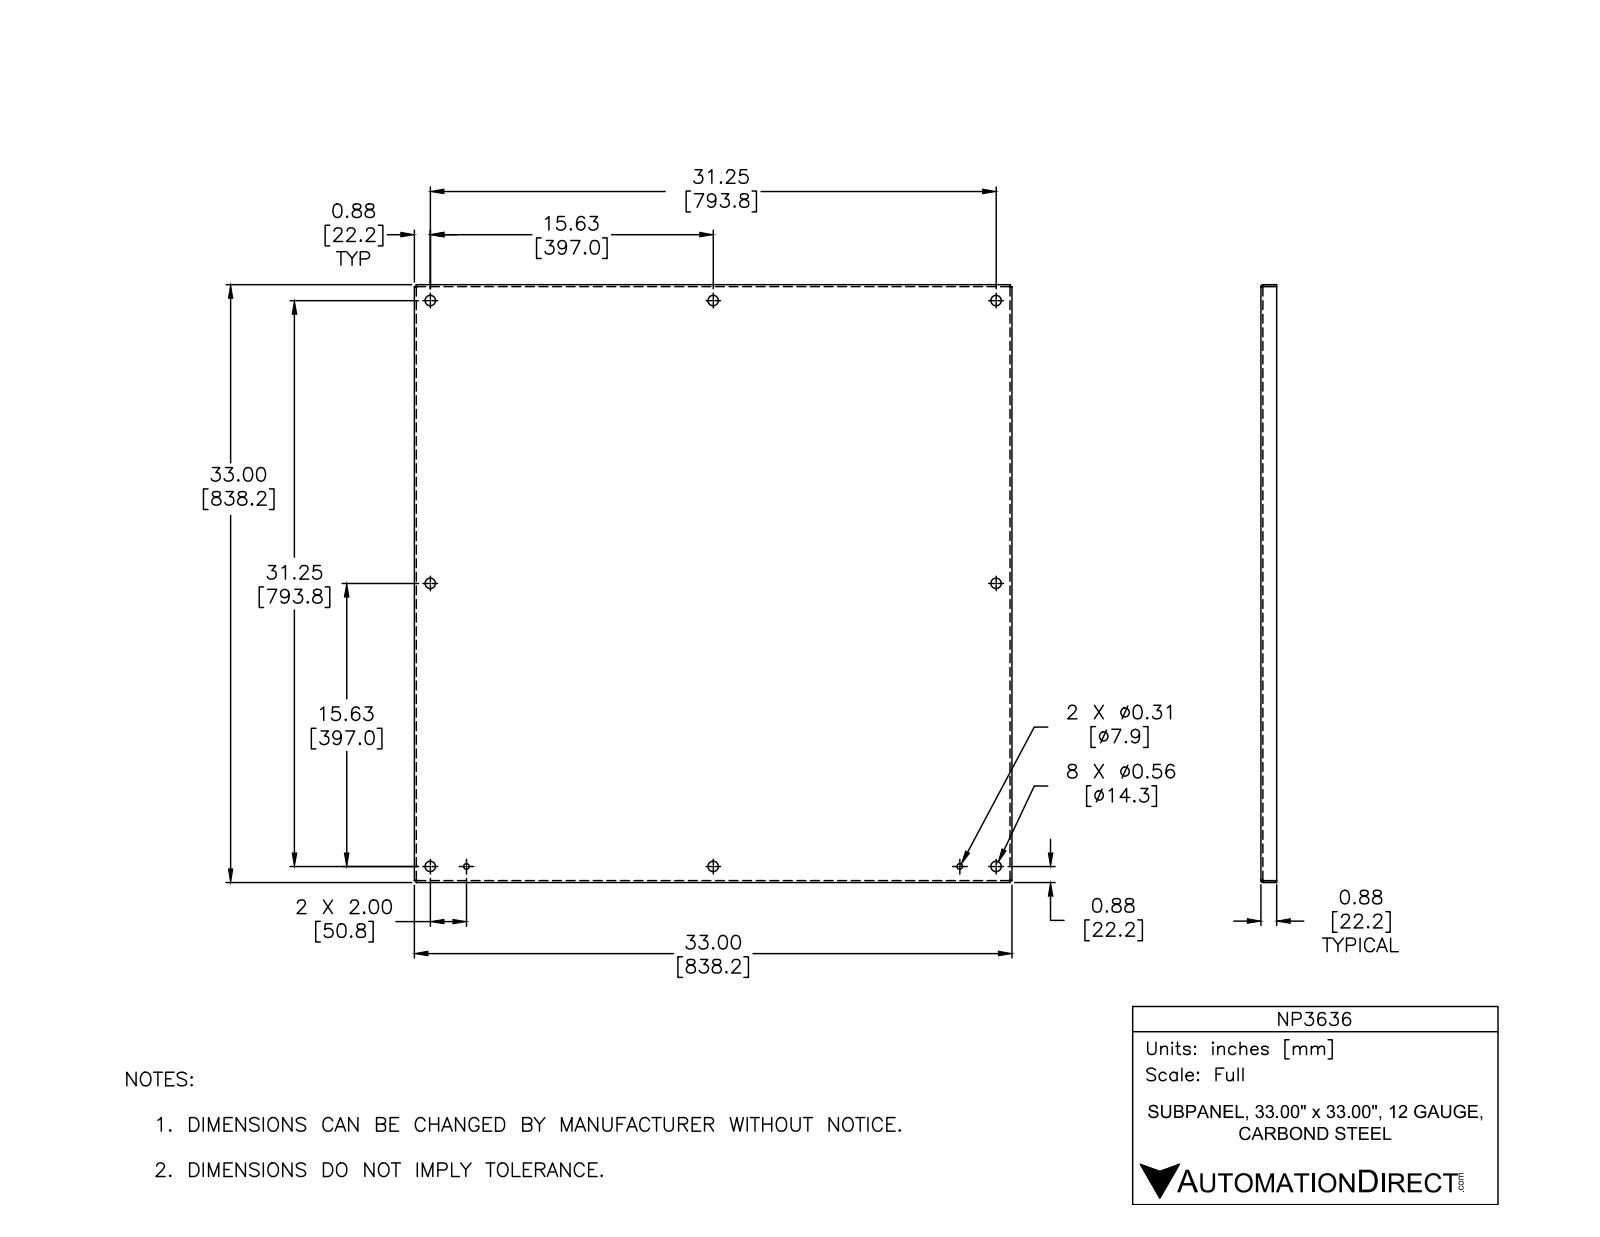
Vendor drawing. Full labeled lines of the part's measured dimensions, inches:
Part name (STEP PRODUCT): NP3636
STEP written by: Autodesk Inventor 2012 (AUTOMOTIVE_DESIGN)
Units: inches
Bodies: 1 solid, 48 faces (22 planar, 18 cylindrical, 8 other)
Overall size (bounding box): 33 × 33 × 0.875
Volume: 111.1 in³ · Surface area: 2 384 in²
Round holes (diameter × count): ⌀0.563 ×8, ⌀0.312 ×2
Partial cylindrical surfaces — rounded edges, fillets, slot ends (radius × count): R0.031 ×4, R0.125 ×4
Main face-to-face distances: 0.094, 32.906, 33, 32.813, 0.781, 0.875, 0.105, 32.895, 32.802, 32.791
Hole centre spacings: 34.939, 31.25, 15.625, 15.625, 22.097, 15.753, 31.314, 34.939
